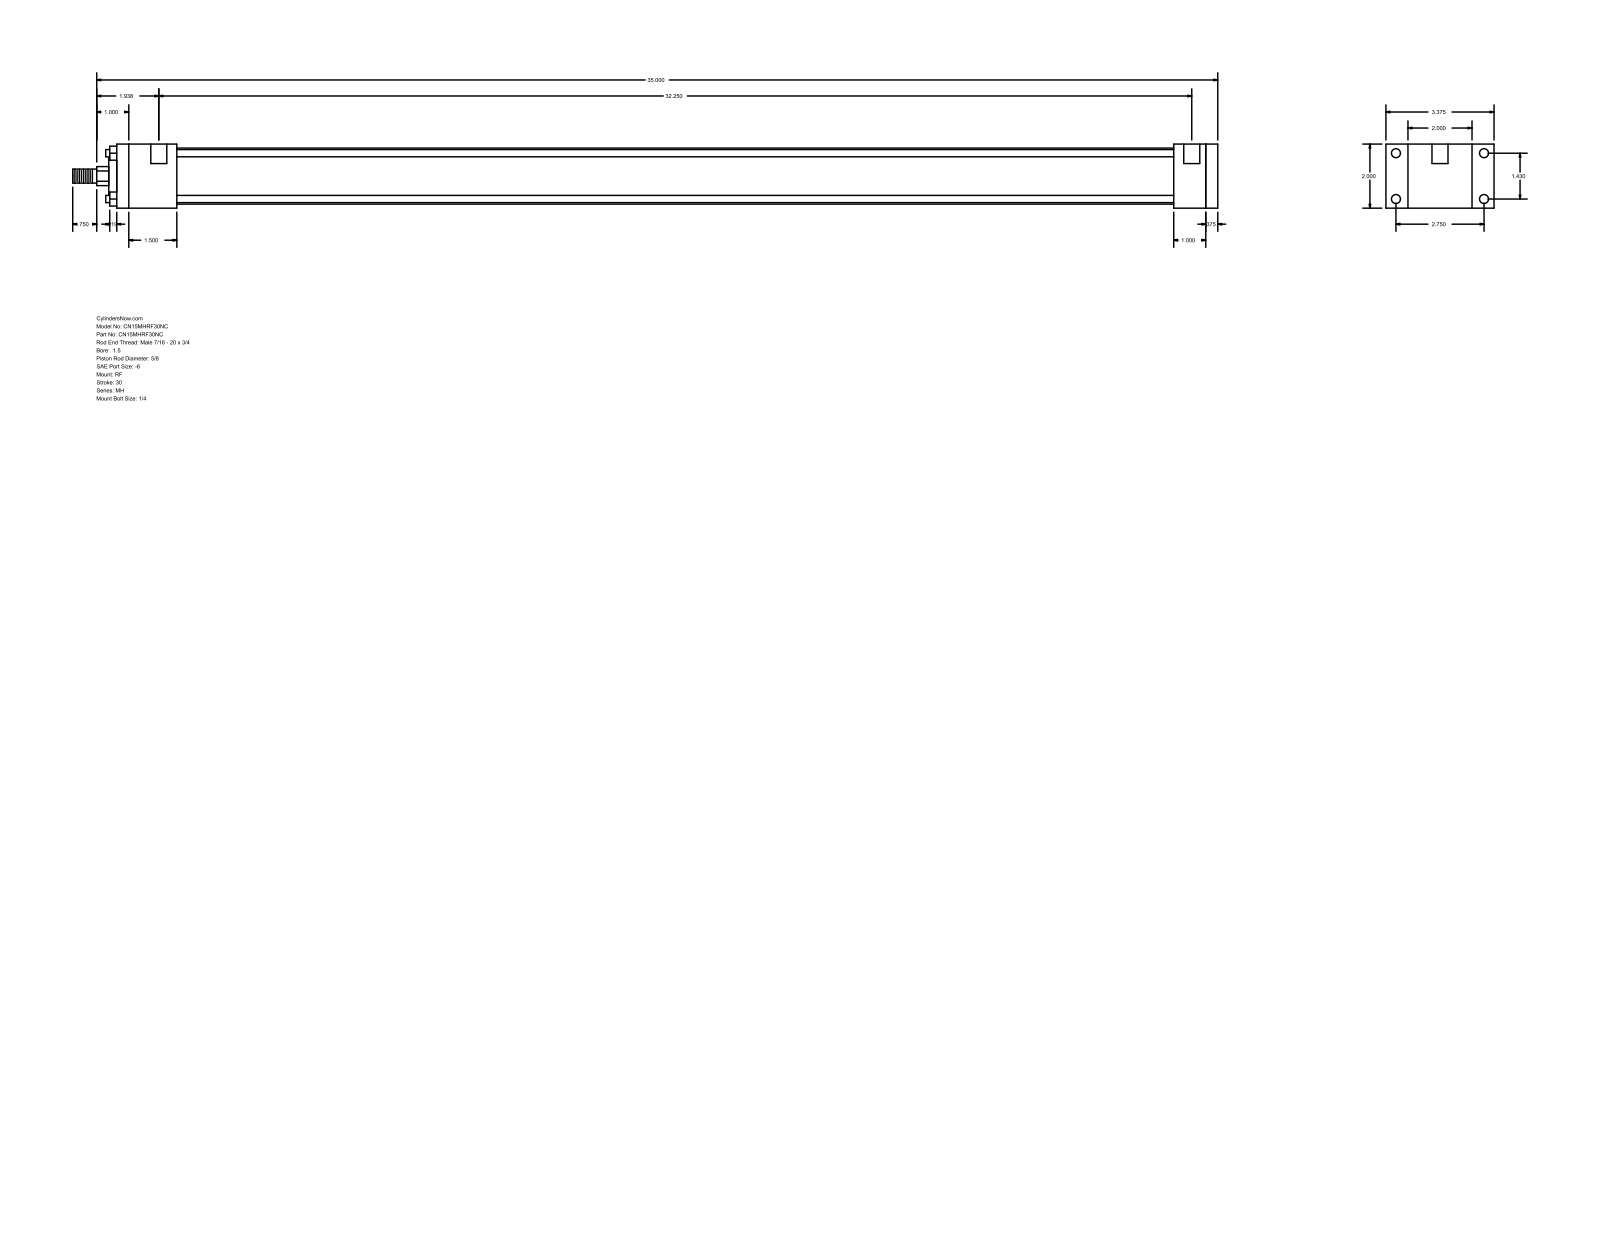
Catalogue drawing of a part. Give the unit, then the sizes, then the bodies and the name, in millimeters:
Units: millimetres
Overall size (bounding box): 908.05 × 85.72 × 50.8
Round holes (diameter × count): ⌀5.56 ×4, ⌀7.14 ×4, ⌀12.7 ×2
Round bosses / shafts (diameter × count): ⌀5.71 ×4, ⌀44.45 ×1, ⌀28.57 ×1, ⌀15.88 ×1, ⌀11.11 ×1
Partial cylindrical surfaces — rounded edges, fillets, slot ends (radius × count): R7.54 ×1
Main face-to-face distances: 50.8, 9.52, 863.6, 873.12, 25.4, 17.46, 68.26, 838.2, 34.92, 47.62
Hole centre spacings: 36.32, 69.84, 78.72, 822.32, 3.17, 819.15
Bodies: 0 solids, 92 faces (64 planar, 28 cylindrical, 0 other)
Part name (STEP PRODUCT): MH_RF__0150_0.625
STEP written by: GSSL Pune (CONFIG_CONTROL_DESIGN)
